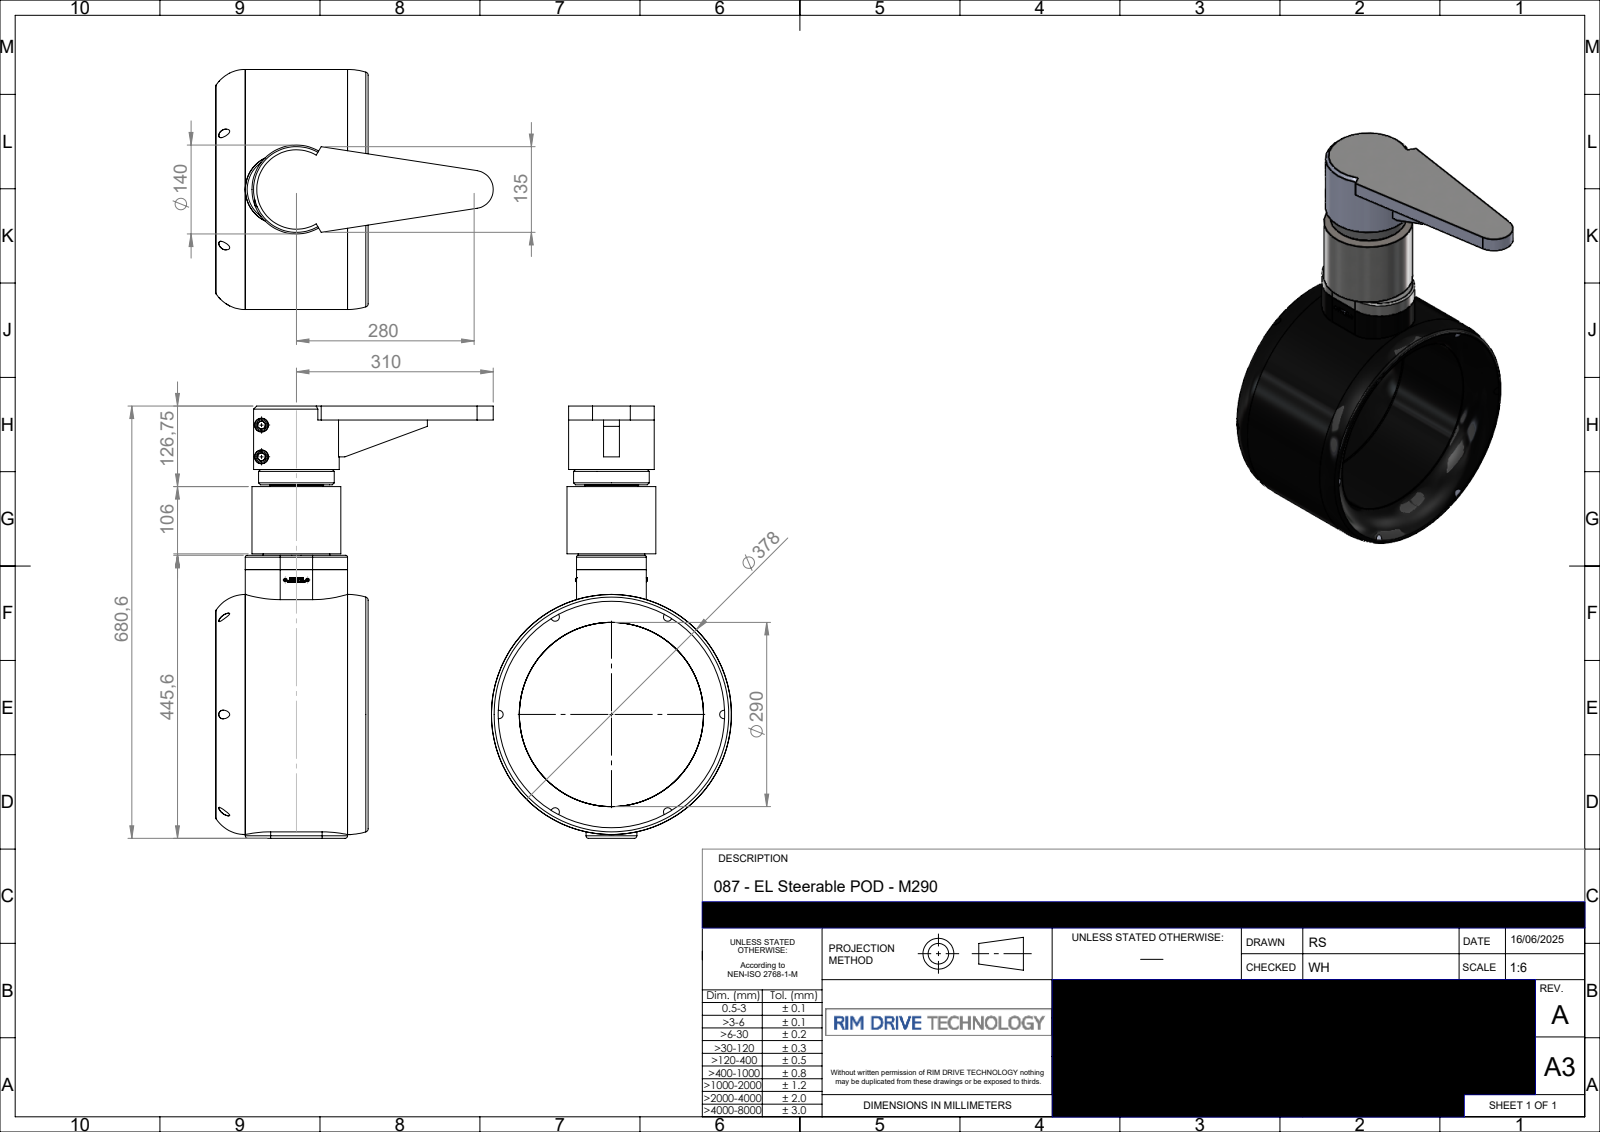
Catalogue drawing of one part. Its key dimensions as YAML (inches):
part_name: "P-087-330-rev-A-M290"
step_written_by: "SolidWorks 2024 (AUTOMOTIVE_DESIGN)"
units: inches
bodies: {solids: 3, faces: 691, planar: 458, cylindrical: 46, other: 187}
overall_size: [26.795, 17.215, 14.882]
volume: 912.9
surface_area: 1202
round_holes:
  - {diameter: 0.138, count: 2}
  - {diameter: 0.472, count: 2}
  - {diameter: 0.866, count: 2}
  - {diameter: 2.756, count: 1}
  - {diameter: 11.417, count: 1}
round_bosses_or_shafts:
  - {diameter: 0.827, count: 2}
  - {diameter: 0.456, count: 2}
  - {diameter: 0.224, count: 2}
  - {diameter: 14.882, count: 1}
  - {diameter: 5.512, count: 1}
  - {diameter: 5.315, count: 1}
  - {diameter: 4.685, count: 1}
  - {diameter: 4.134, count: 1}
partial_cylinders:
  - {radius: 0.157, count: 4}
  - {radius: 0.197, count: 4}
  - {radius: 0.004, count: 2}
  - {radius: 0.118, count: 2}
  - {radius: 1.575, count: 2}
  - {radius: 2.165, count: 2}
  - {radius: 1.181, count: 1}
face_to_face_distances: [0.866, 4.124, 4.99, 21.805, 25.929, 26.795, 17.632, 4.173, 8.297, 9.163]
hole_center_spacings: [1.378, 1.969, 7.773, 8.148, 9.713, 10.016]
